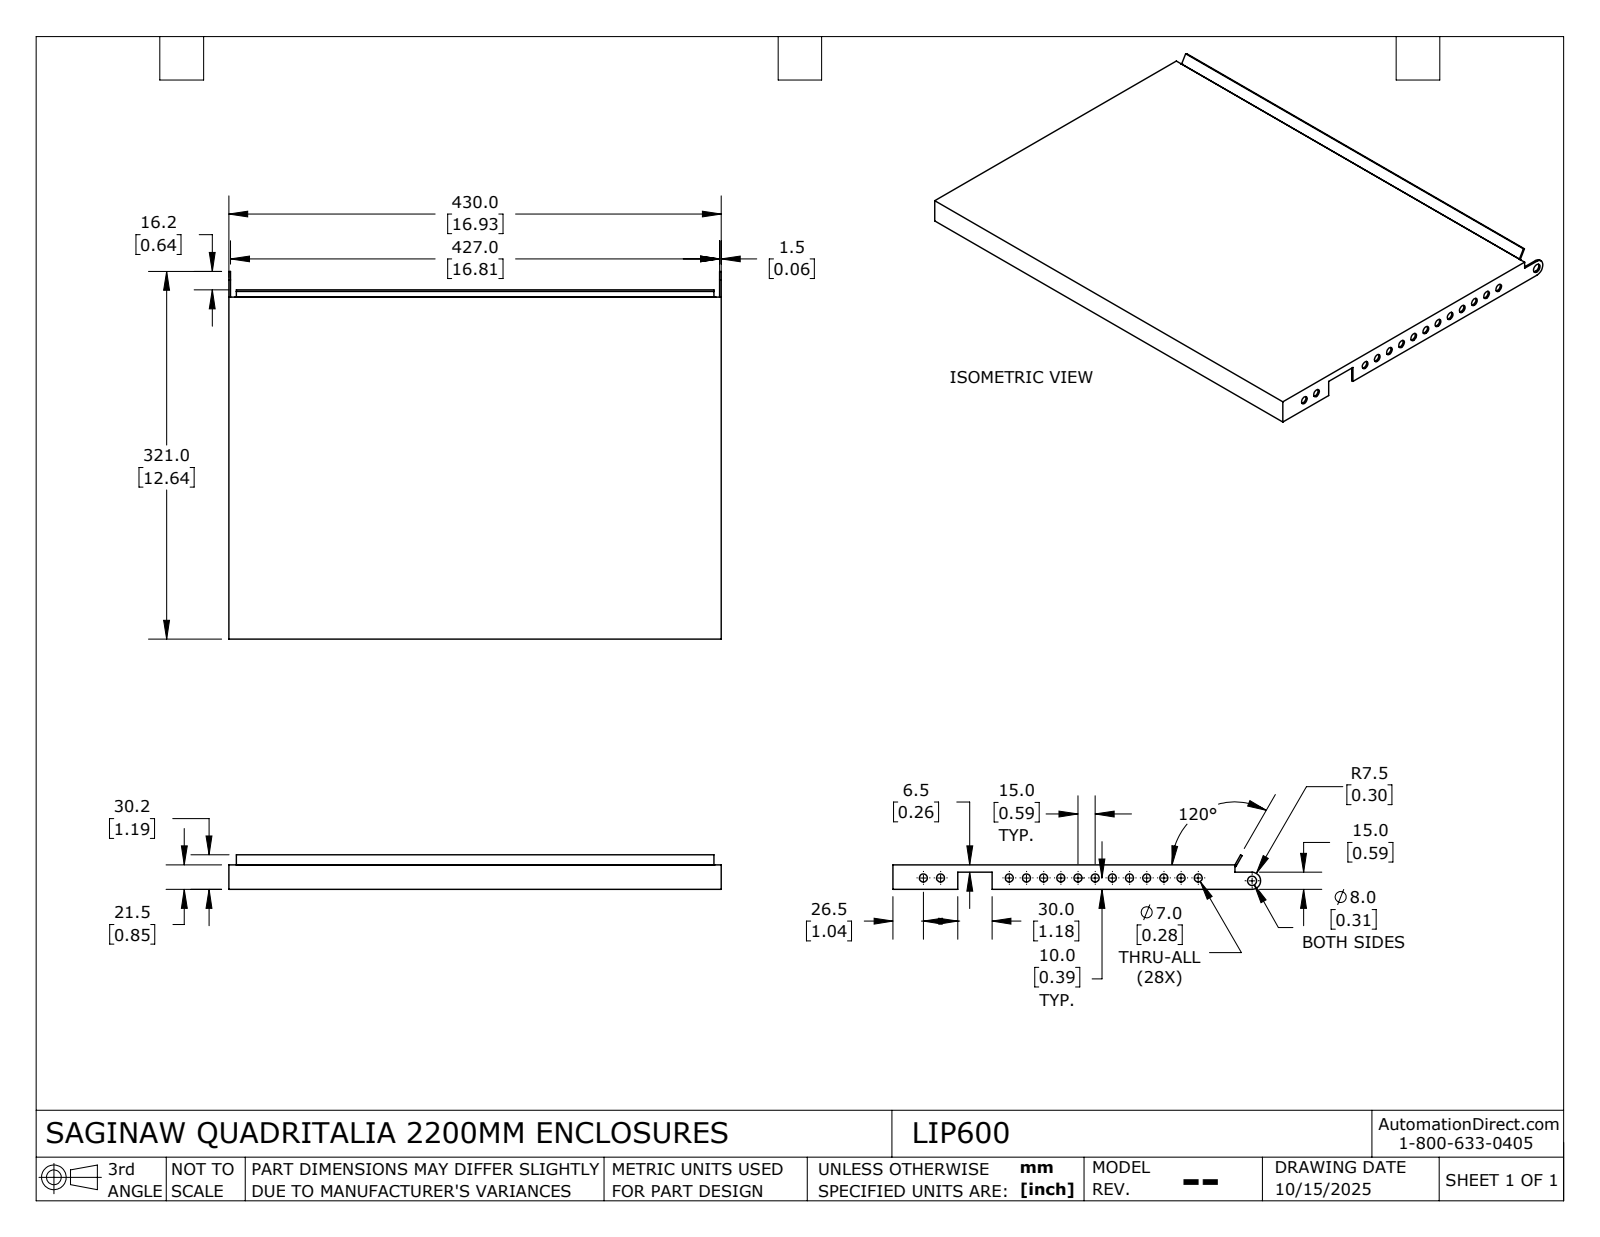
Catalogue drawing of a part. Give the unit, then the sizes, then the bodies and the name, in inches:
Units: inches
Overall size (bounding box): 16.929 × 12.638 × 1.187
Round holes (diameter × count): ⌀0.276 ×14, ⌀0.315 ×1
Partial cylindrical surfaces — rounded edges, fillets, slot ends (radius × count): R0.157 ×2, R0.295 ×1
Main face-to-face distances: 0.059, 16.87, 16.929, 16.811, 0.787, 0.846, 0.256, 0.197, 0.591, 2.224
Hole centre spacings: 0.591, 1.181, 1.772, 2.362, 2.953, 3.543, 4.134, 4.724
Volume: 13.91 in³ · Surface area: 476.3 in²
Bodies: 1 solid, 70 faces (32 planar, 38 cylindrical, 0 other)
Part name (STEP PRODUCT): LIP600_Default
STEP written by: SolidWorks 2024 (CONFIG_CONTROL_DESIGN)
